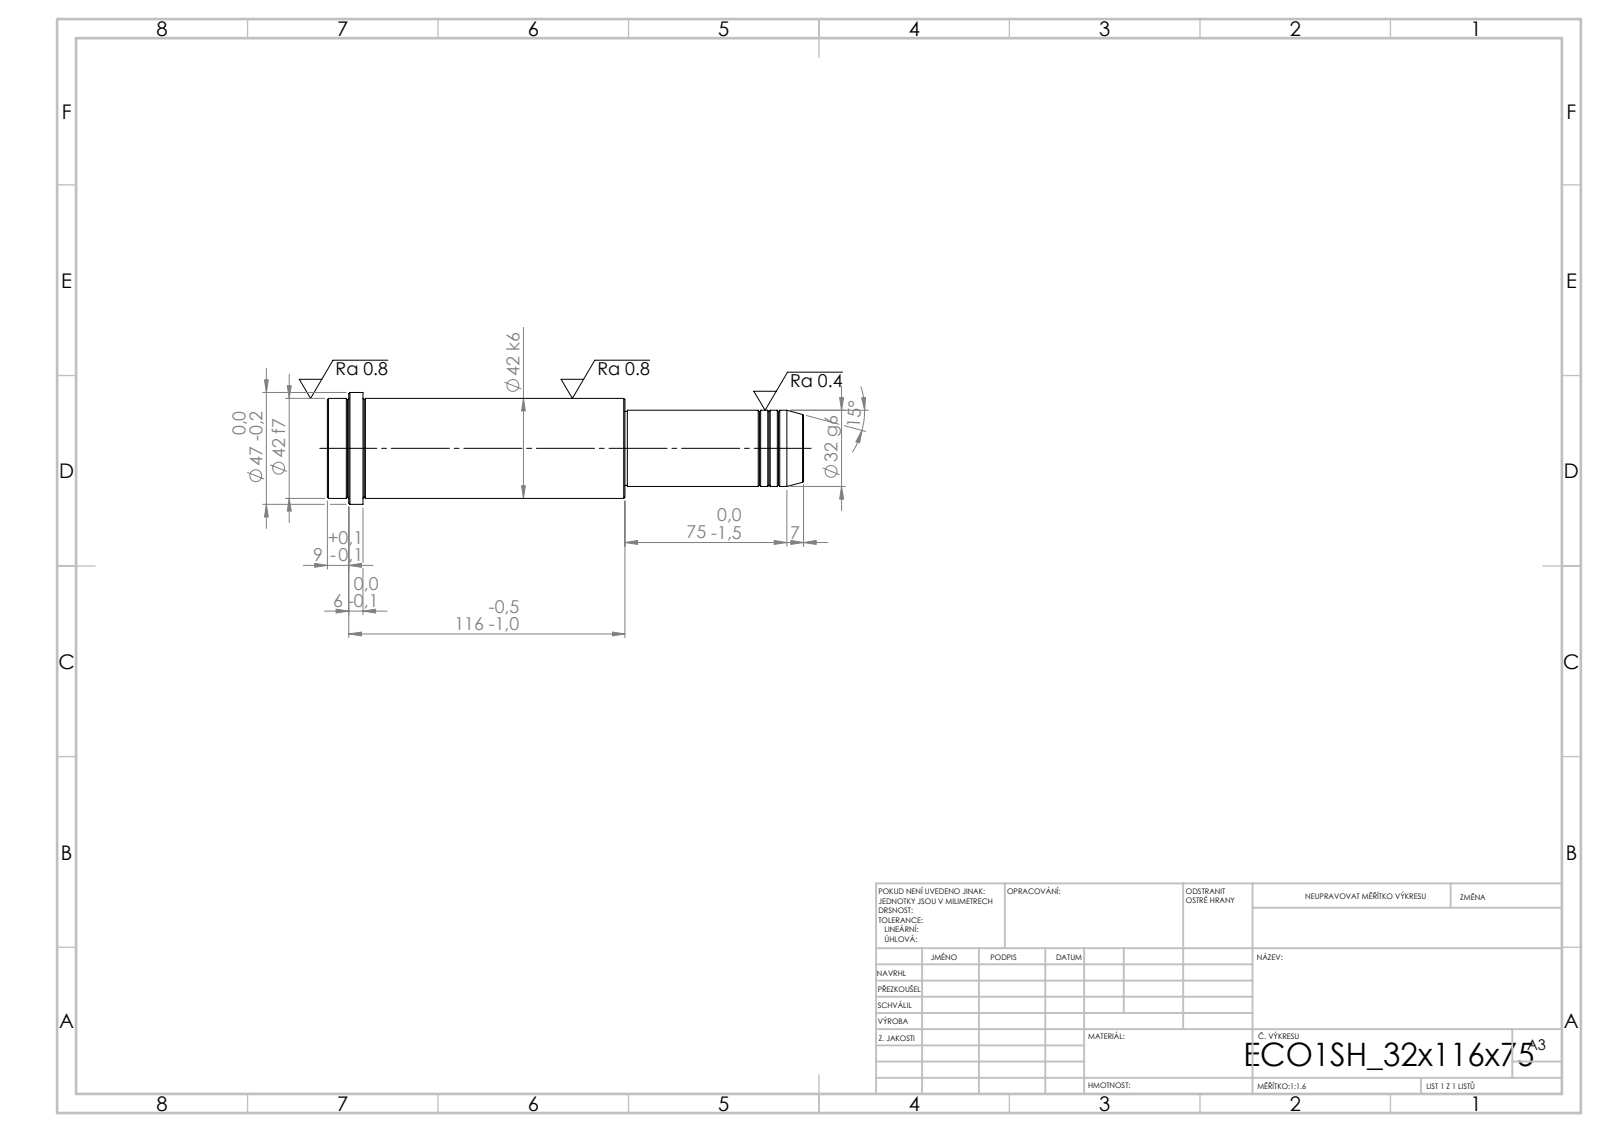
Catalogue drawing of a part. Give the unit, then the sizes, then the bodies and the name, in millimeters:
Units: millimetres
Overall size (bounding box): 200 × 47 × 47
Round bosses / shafts (diameter × count): ⌀47 ×1, ⌀42 ×1, ⌀32 ×1, ⌀31 ×1
Main face-to-face distances: 200, 75, 125, 185, 110, 15, 191, 116, 6, 9
Volume: 234 639 mm³ · Surface area: 27 673 mm²
Bodies: 1 solid, 52 faces (6 planar, 16 cylindrical, 30 other)
STEP written by: SolidWorks 2019 (CONFIG_CONTROL_DESIGN)
